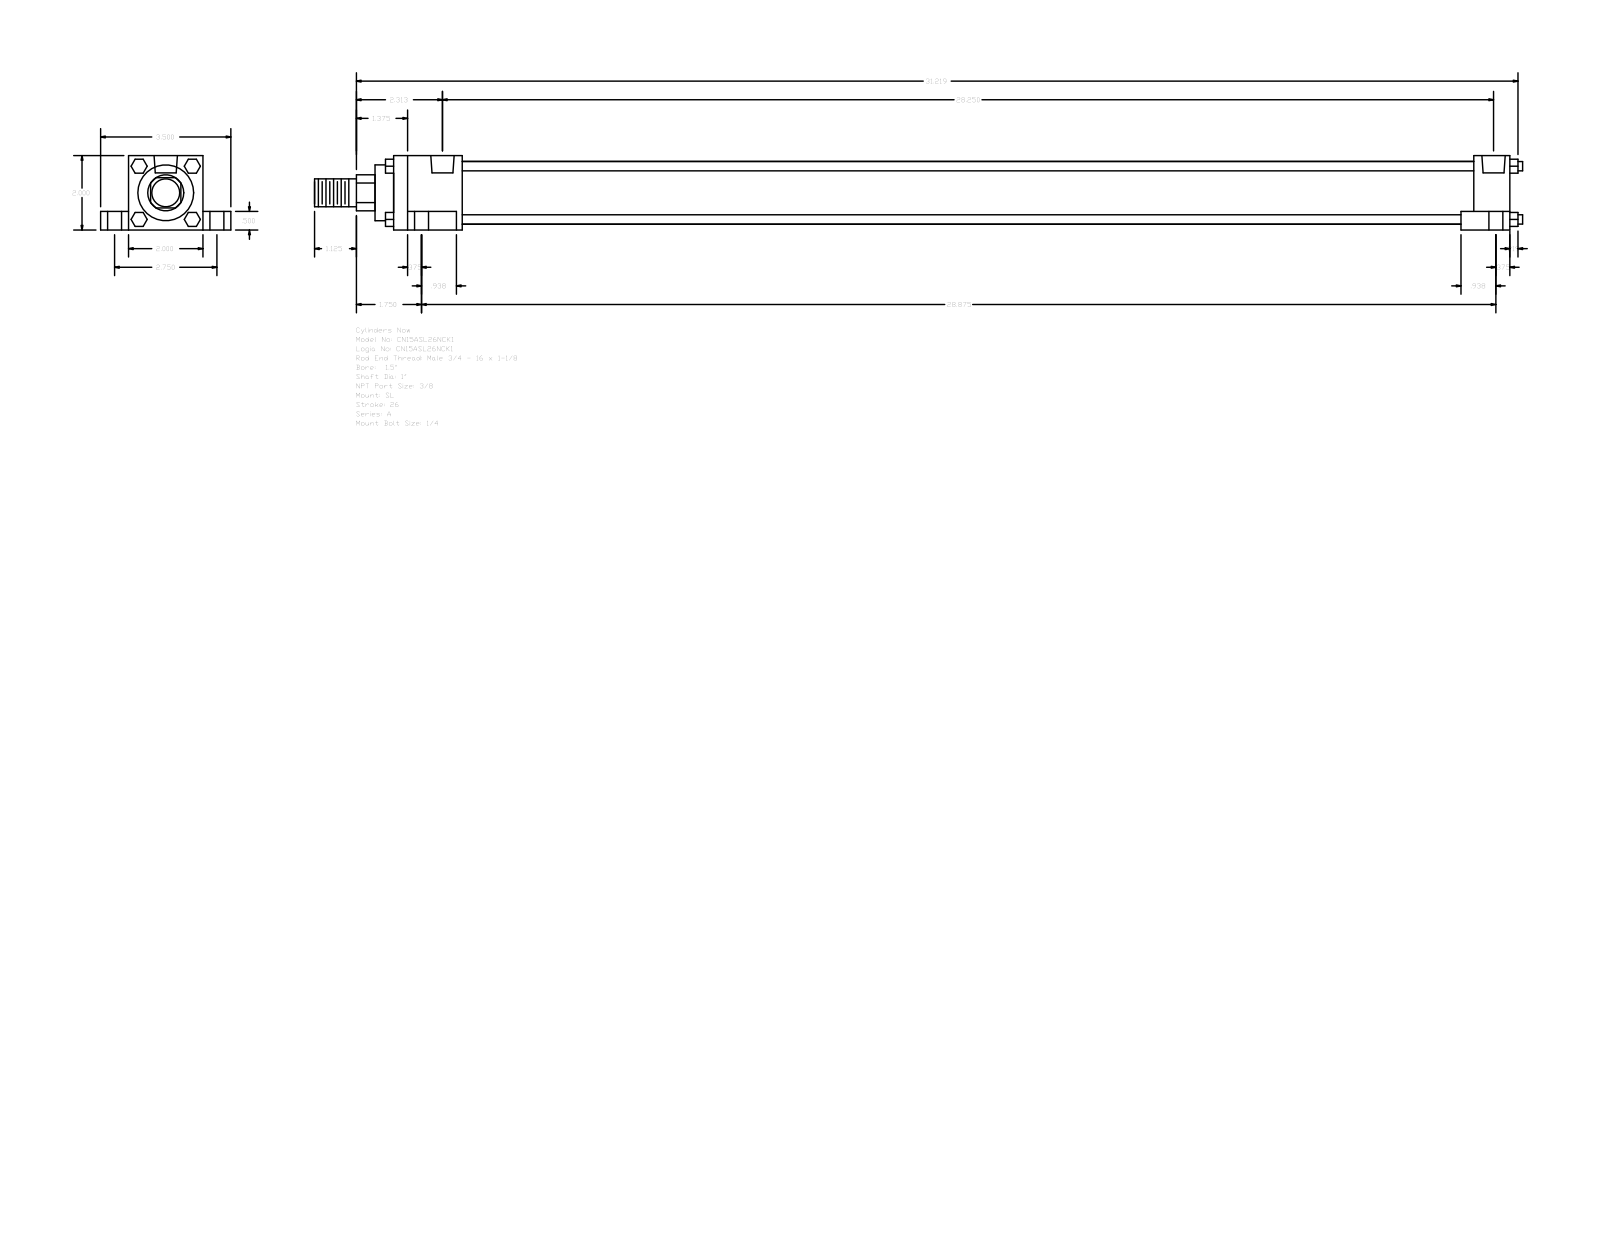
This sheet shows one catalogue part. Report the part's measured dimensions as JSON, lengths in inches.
{"part_name": "A_SL__0150_1", "step_written_by": "GSSL Pune (CONFIG_CONTROL_DESIGN)", "units": "inches", "bodies": {"solids": 0, "faces": 148, "planar": 112, "cylindrical": 36, "other": 0}, "overall_size": [32.469, 3.5, 2], "round_holes": [[0.219, 4], [0.375, 4], [0.625, 4], [0.627, 2]], "round_bosses_or_shafts": [[0.25, 4], [1.69, 1], [1.5, 1], [1, 1], [0.75, 1]], "partial_cylinders_radius": [[0.484, 1]], "face_to_face_distances": [2, 0.5, 1.5, 0.75, 2.75, 0.375, 30, 1.313, 29.031, 0.969], "hole_center_spacings": [0.156, 1.376, 1.392, 1.485, 1.552, 2.75, 27.937, 28.094]}
